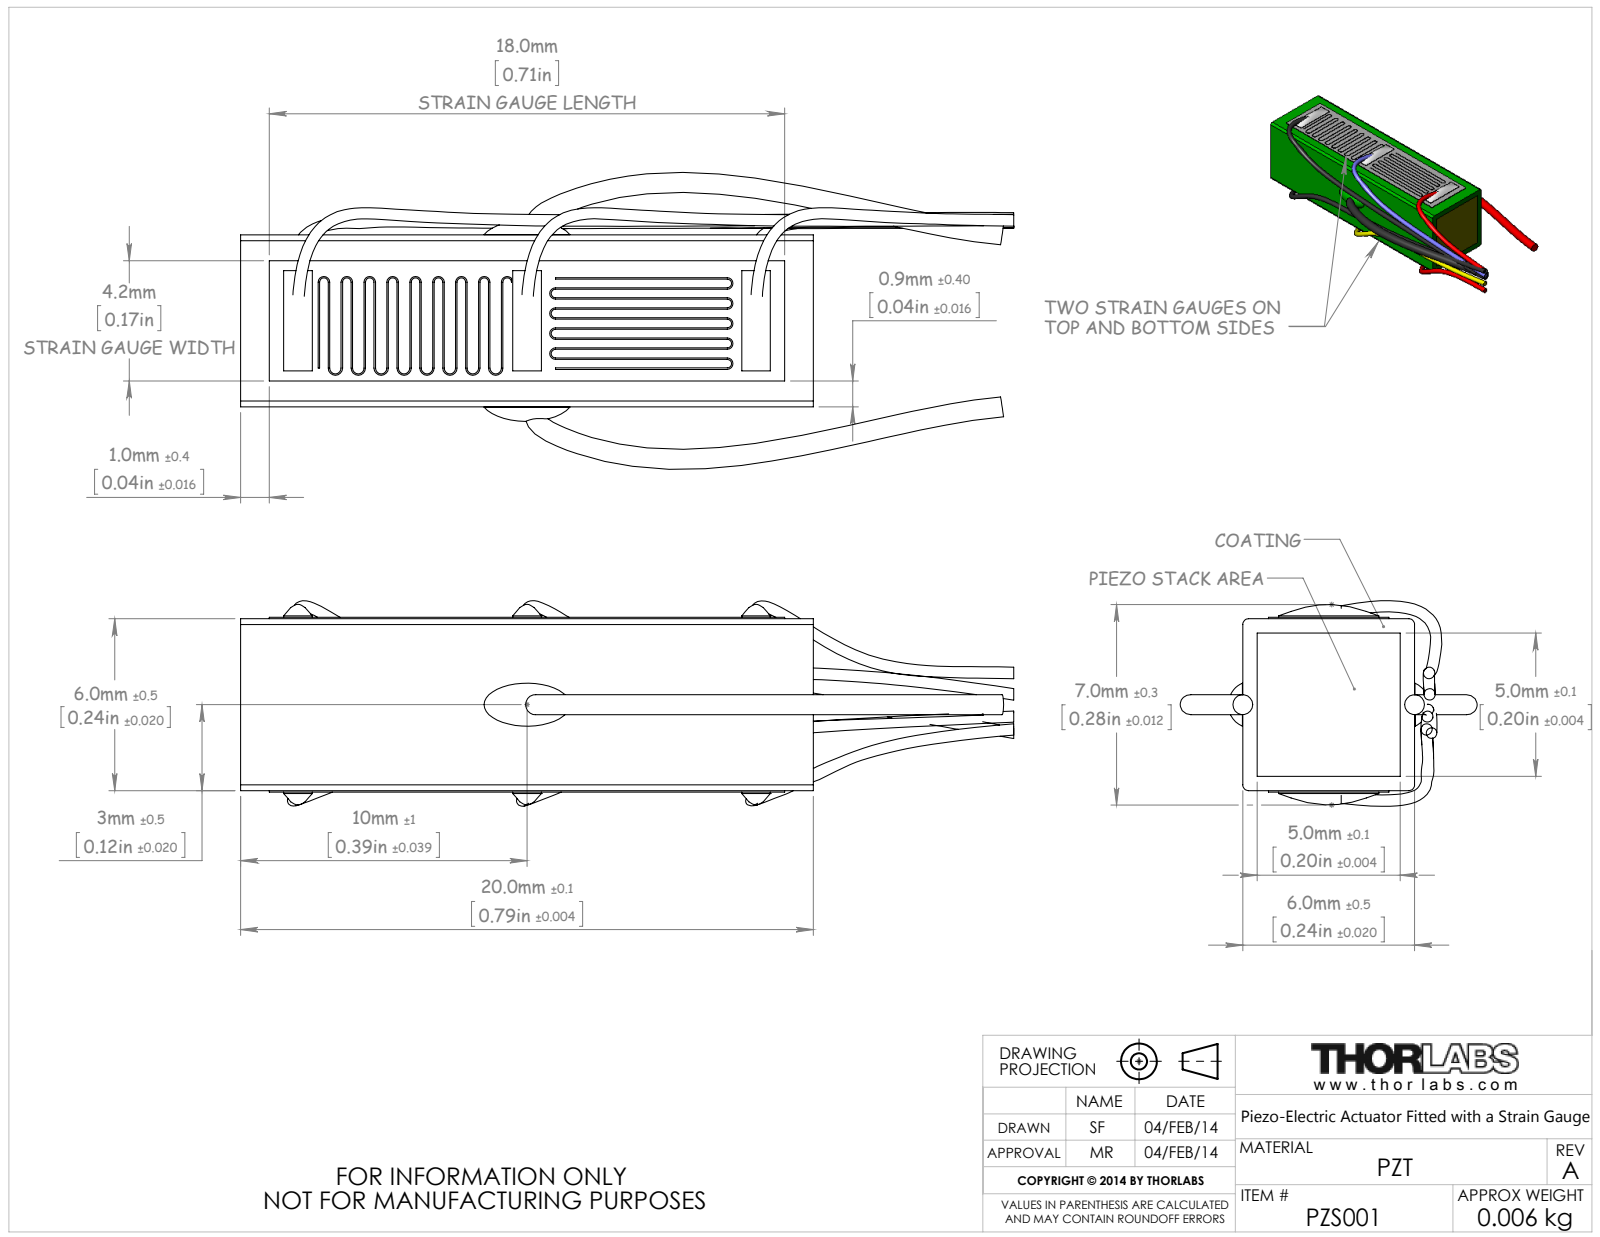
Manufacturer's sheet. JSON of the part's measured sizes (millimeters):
{"part_name": "PZS001", "step_written_by": "SolidWorks 2012 (AUTOMOTIVE_DESIGN)", "units": "millimeters", "bodies": {"solids": 9, "faces": 94, "planar": 62, "cylindrical": 4, "other": 28}, "overall_size": [27.11, 10.37, 7.18], "volume_mm3": 761, "surface_area_mm2": 1083, "partial_cylinders_radius": [[0.2, 4]], "face_to_face_distances": [6, 6.05, 6.1, 20, 0.9, 5.1, 1, 8, 4.2, 17.5]}
